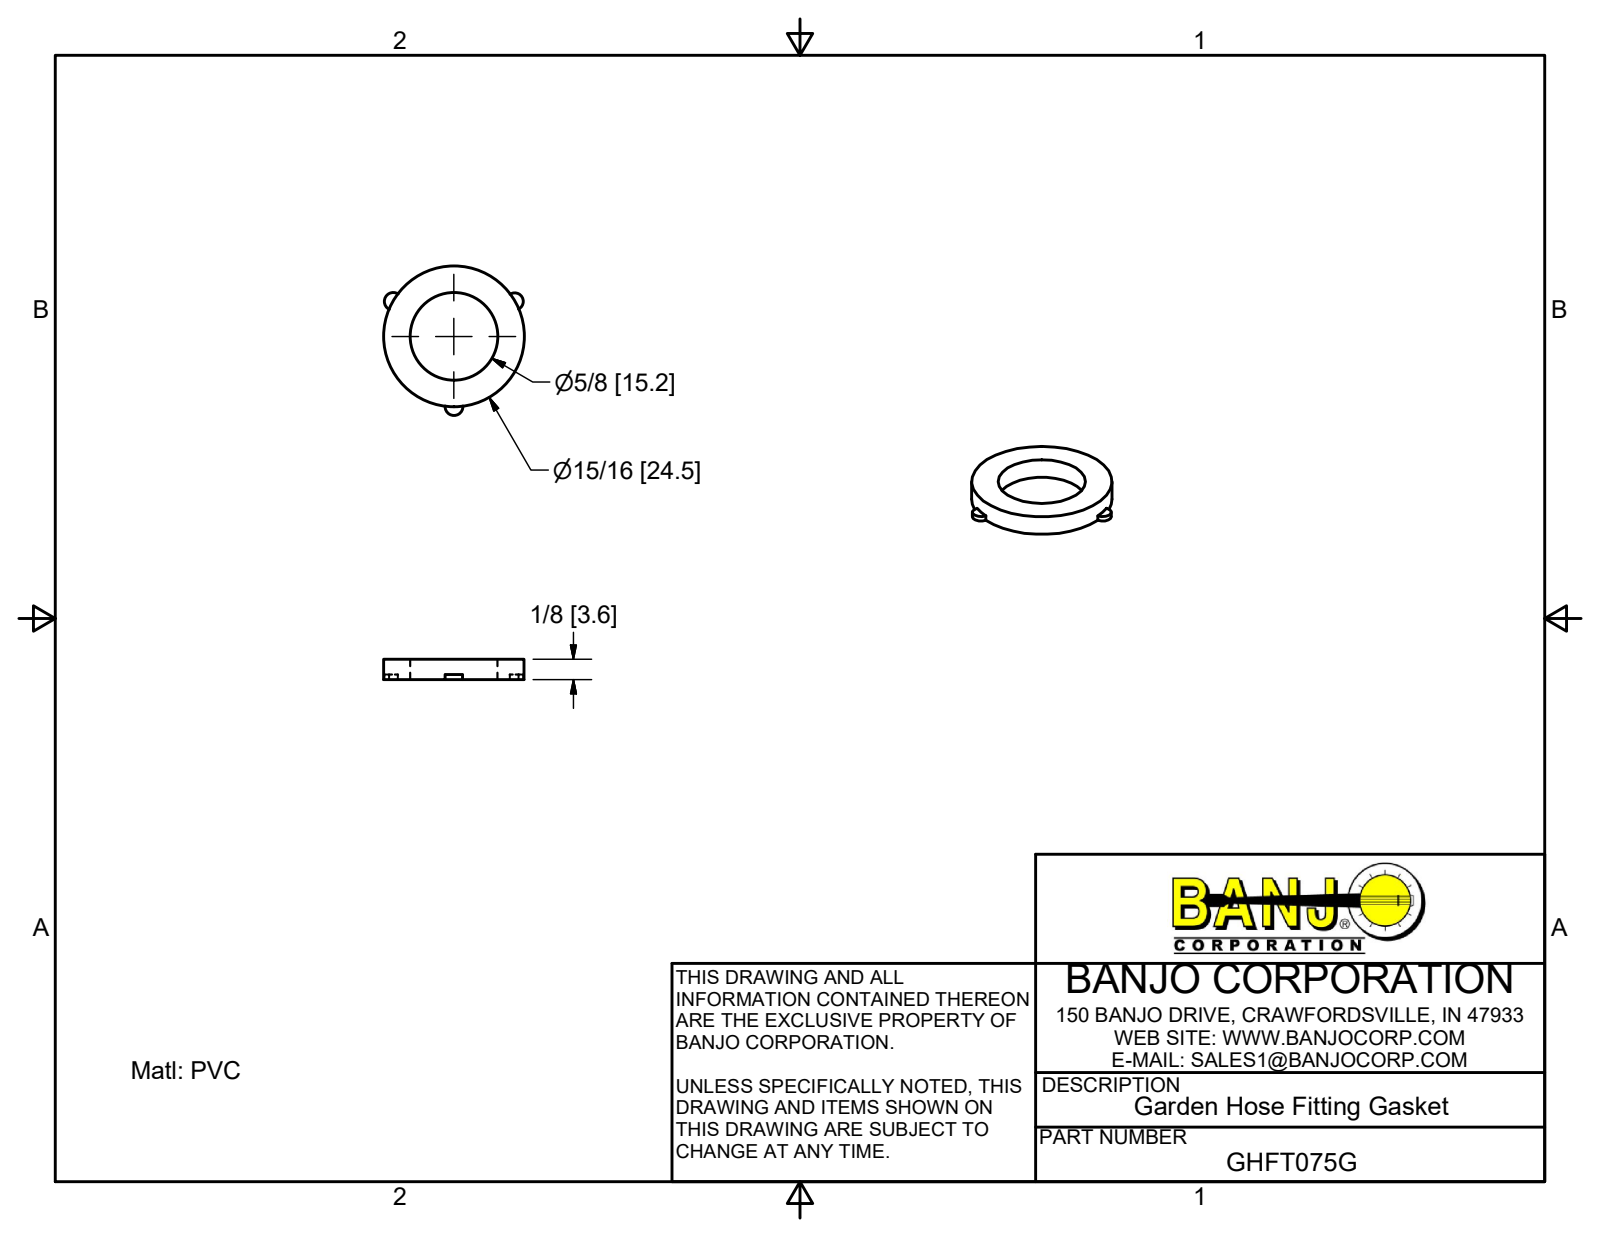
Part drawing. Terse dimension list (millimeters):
name: GHFT075G
written by: Autodesk Inventor 2017 (AUTOMOTIVE_DESIGN)
unit: mm
bodies: 1 solid, 10 faces (5 planar, 5 cylindrical, 0 other)
size: 26.04 × 24.51 × 3.56
volume: 1 039 mm³; area: 1 051 mm²
holes: 1× ⌀15.24
bosses: 1× ⌀24.51
rounds: 3× R1.52
face distances: 3.56, 0.89, 2.67
